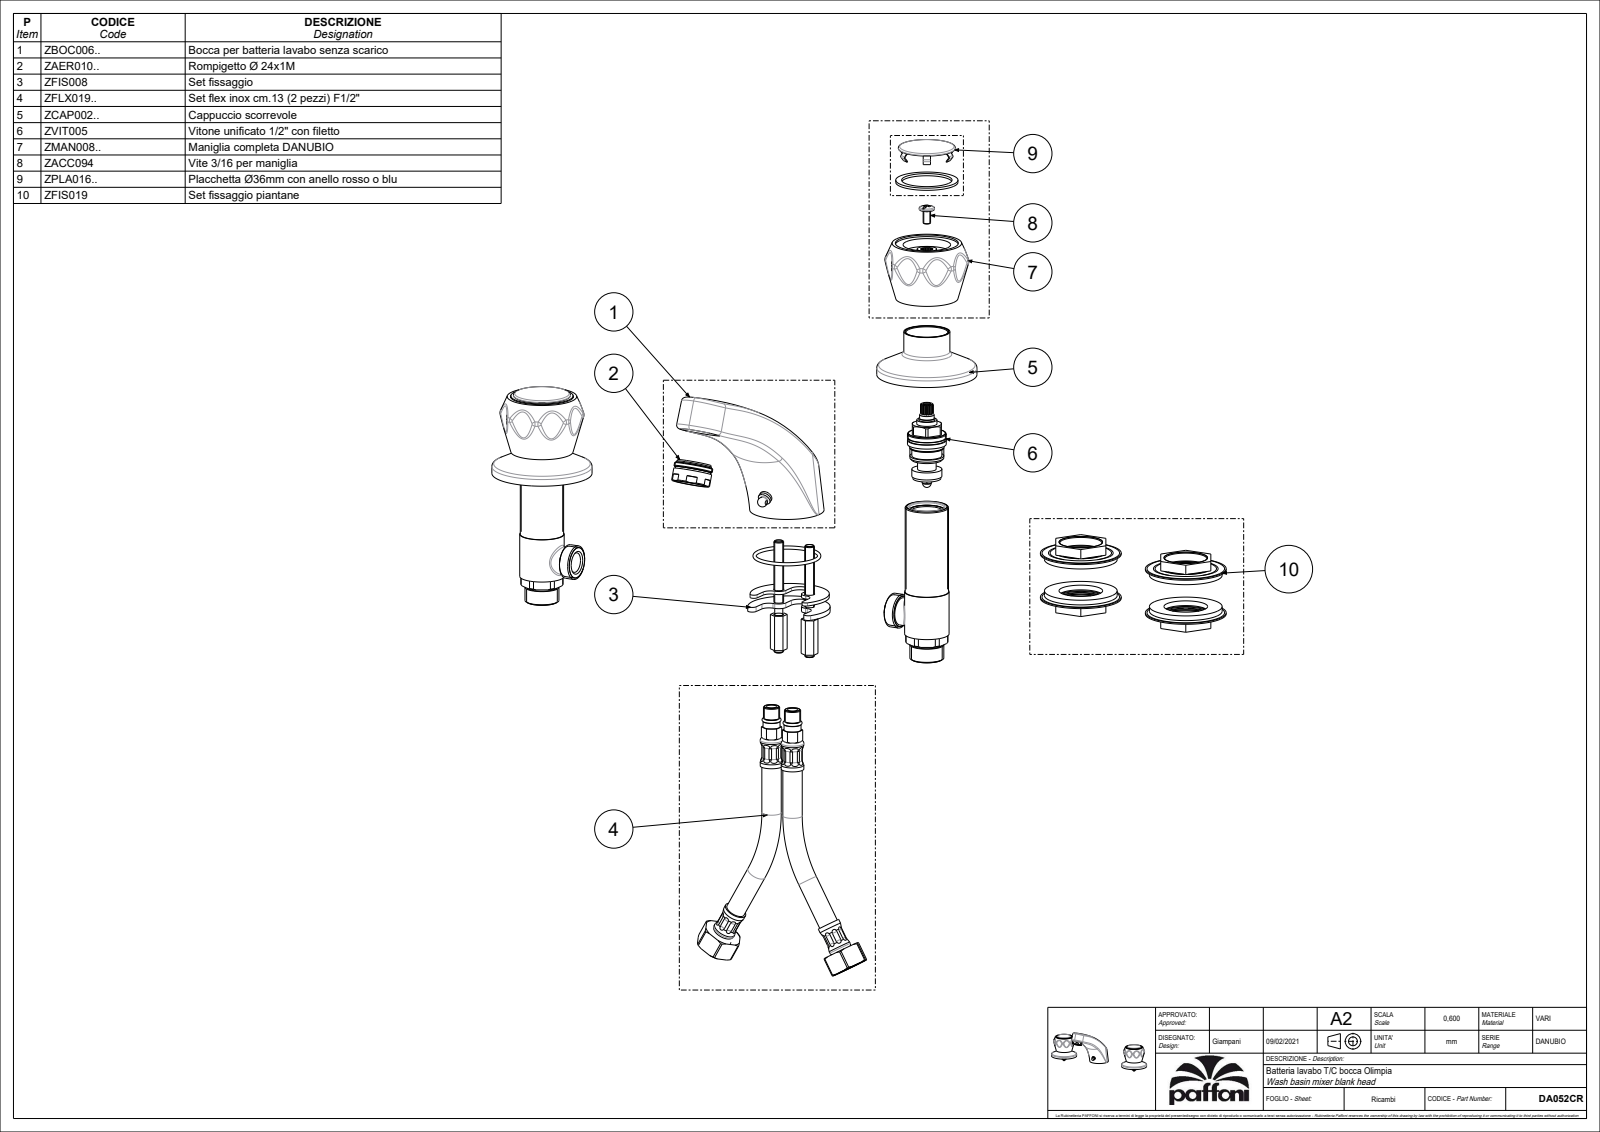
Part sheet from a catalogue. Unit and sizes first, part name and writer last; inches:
Units: inches
Overall size (bounding box): 10.315 × 5.22 × 3.888
Round holes (diameter × count): ⌀0.197 ×2, ⌀0.354 ×2, ⌀0.433 ×2, ⌀0.63 ×1, ⌀0.827 ×1, ⌀0.906 ×1, ⌀1.654 ×1
Round bosses / shafts (diameter × count): ⌀2.441 ×2, ⌀1.516 ×2, ⌀1.496 ×1, ⌀0.937 ×1, ⌀0.866 ×1, ⌀0.315 ×1, ⌀0.177 ×1
Partial cylindrical surfaces — rounded edges, fillets, slot ends (radius × count): R0.839 ×16, R0.059 ×4, R0.197 ×2, R0.295 ×2
Main face-to-face distances: 0.118, 0.543, 1.933, 1.39, 1.949, 1.406, 0.016, 0.236, 0.289, 0.059
Hole centre spacings: 0.378, 0.559, 0.606, 0.938, 0.591, 0.866
Volume: 14.77 in³ · Surface area: 98.06 in²
Bodies: 3 solids, 287 faces (43 planar, 62 cylindrical, 182 other)
Part name (STEP PRODUCT): DA052CR
STEP written by: CREO PARAMETRIC BY PTC INC, 2020044 (CONFIG_CONTROL_DESIGN)
